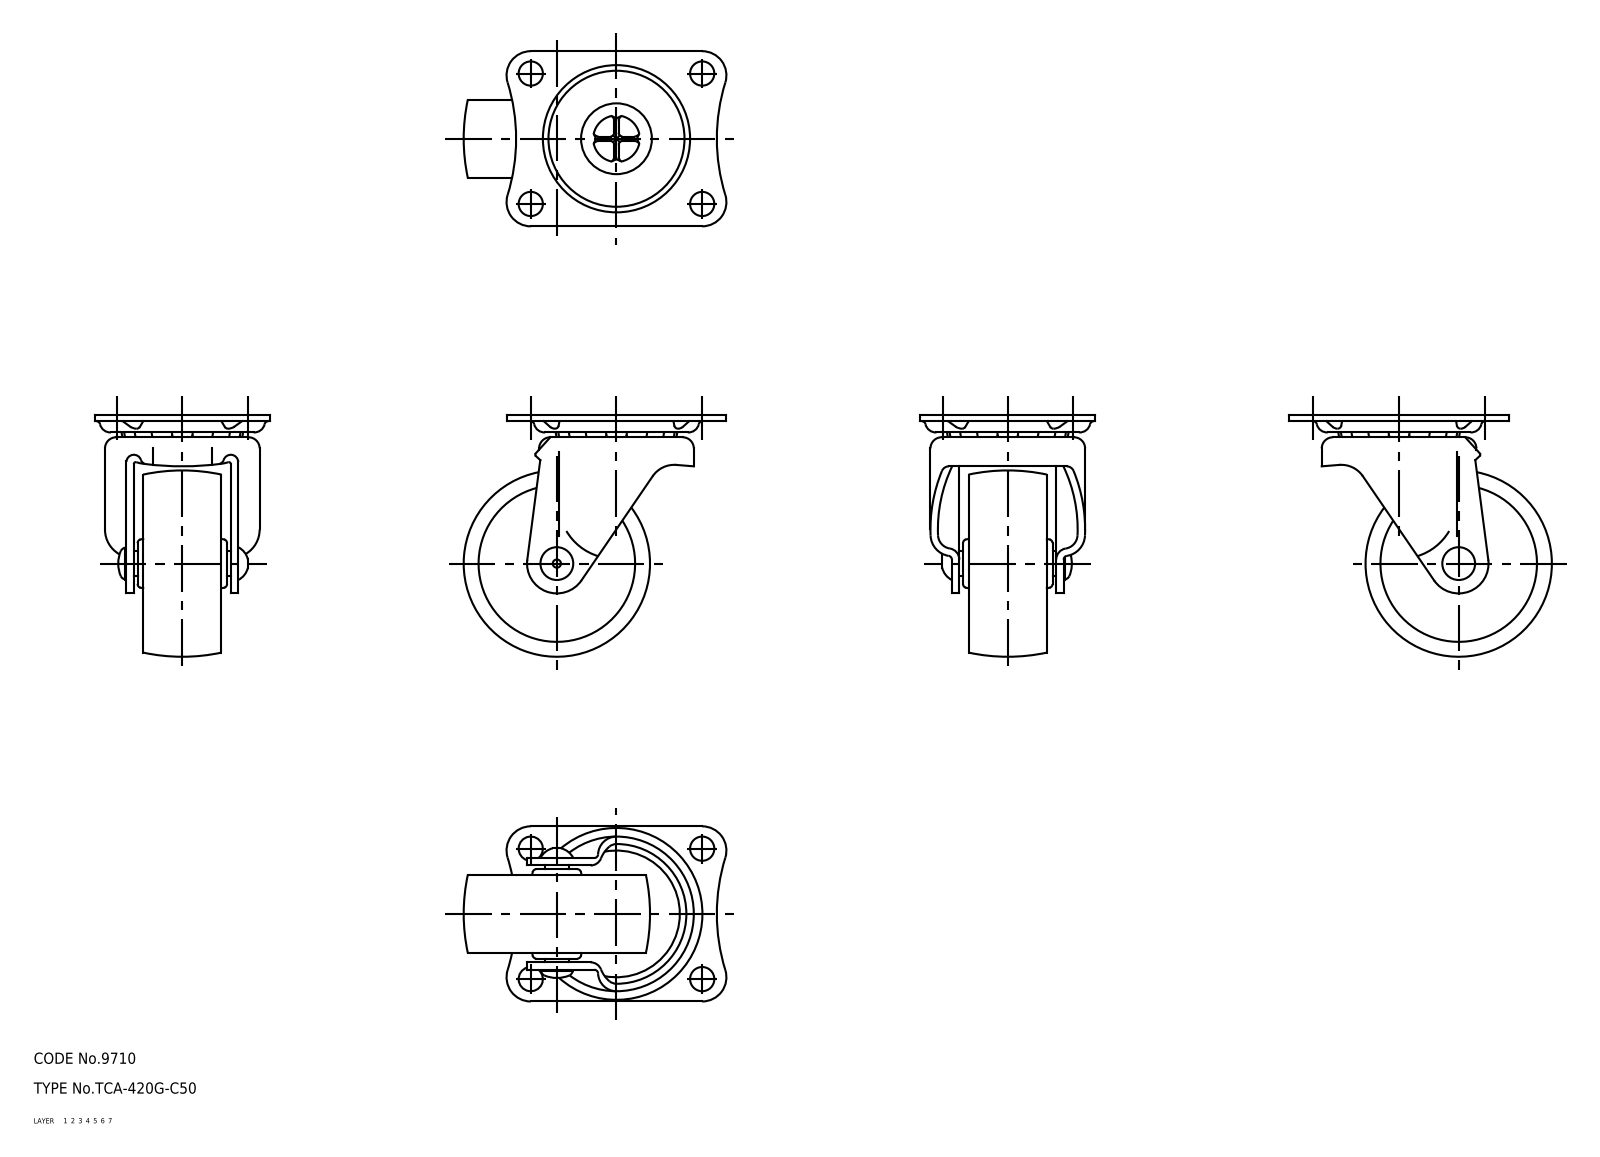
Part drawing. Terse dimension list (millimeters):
name: wheel; mounting plate; main shaft; axle (+1 more)
written by: CADfix (AUTOMOTIVE_DESIGN)
unit: mm
bodies: 5 solids, 290 faces (0 planar, 0 cylindrical, 290 other)
size: 70.5 × 65 × 47
volume: 41 748 mm³; area: 25 542 mm²
